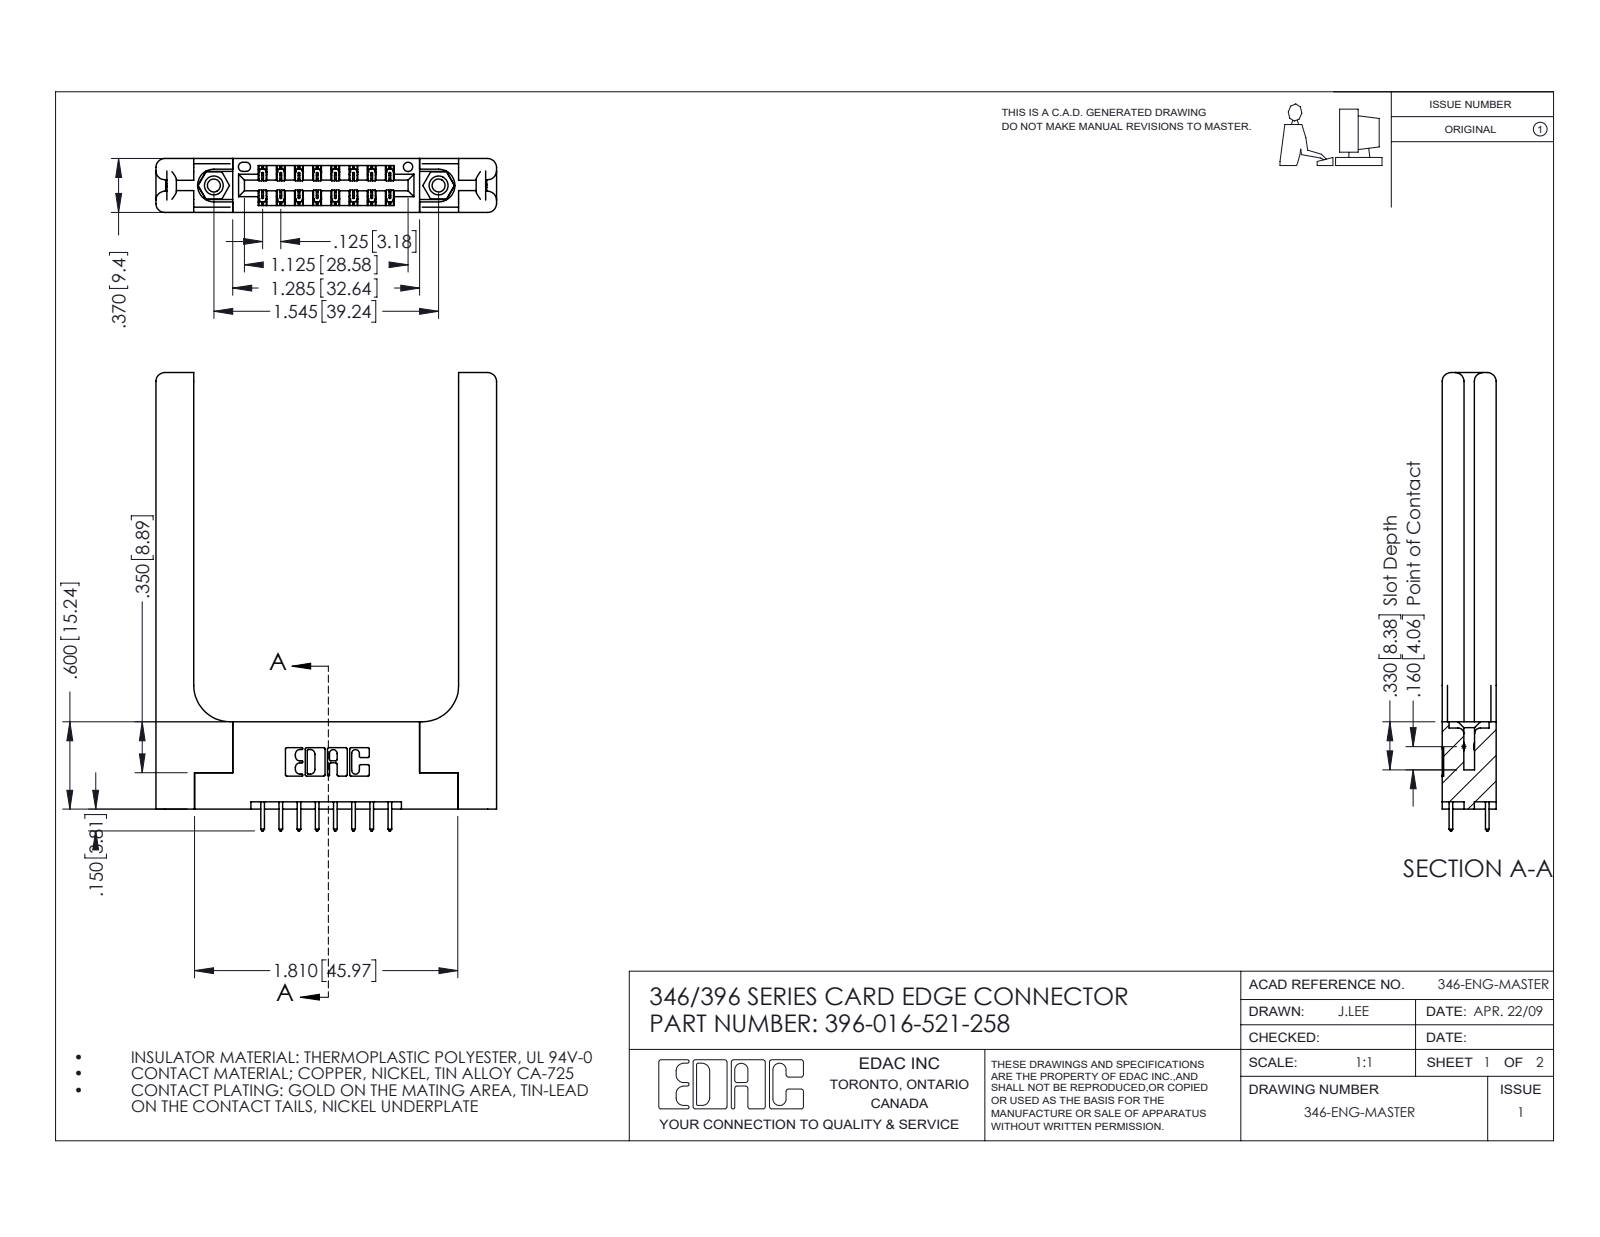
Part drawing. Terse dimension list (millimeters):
name: 345-250-001_345-250-001-102; 345-292-001_345-293-121; 346 Part_Flush Mounting Lugs - 0.156 Dia-TH; 396-016-521-258 (+1 more)
written by: SolidWorks 2016 (CONFIG_CONTROL_DESIGN)
unit: mm
bodies: 21 solids, 1210 faces (784 planar, 366 cylindrical, 60 other)
size: 80 × 59.5 × 9.4
volume: 13 000 mm³; area: 11 990 mm²
holes: 2× ⌀2.3, 2× ⌀3.2, 2× ⌀4, 1× ⌀1.6
bosses: 2× ⌀3.9
rounds: 24× R0.2, 22× R0.3, 16× R0.3, 16× R1.5, 6× R0.2, 6× R0.8, 3× R0.7, 2× R0.4
face distances: 9.4, 3.8, 5.6, 1.8, 3.8, 6.4, 2.6, 1.2, 8.2, 4.4
hole spacings: 6.2, 34.1, 39.2
